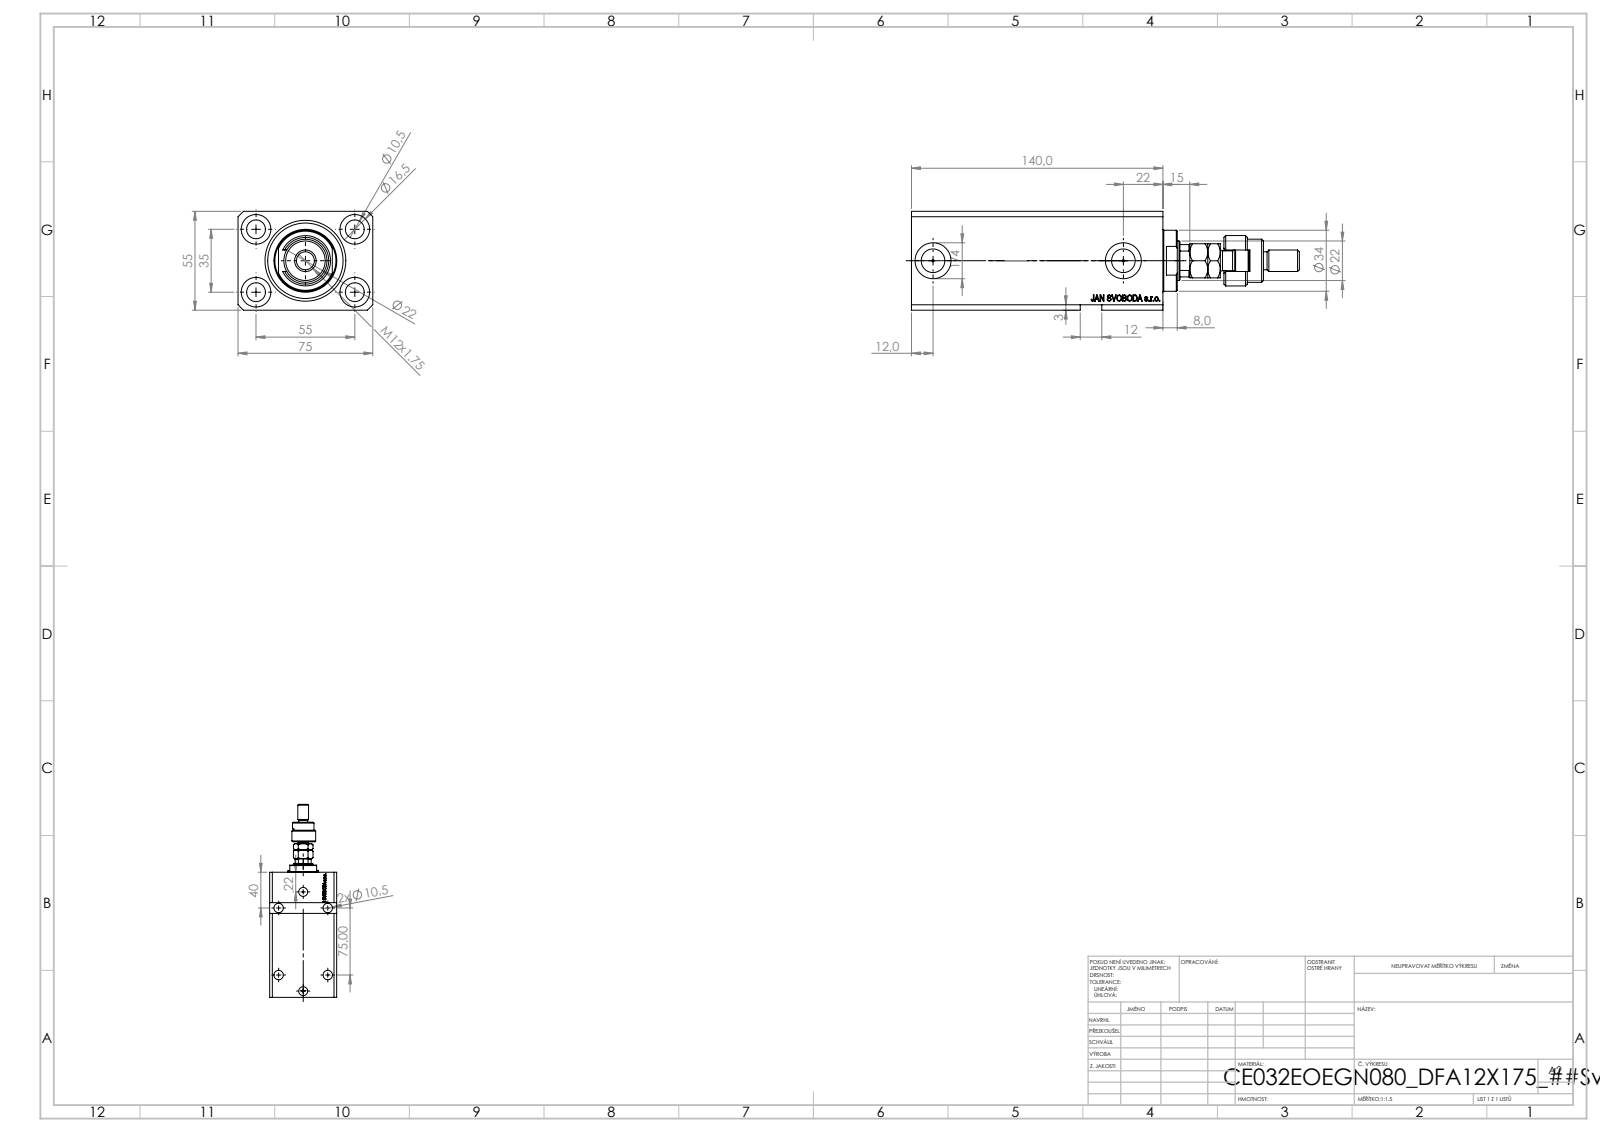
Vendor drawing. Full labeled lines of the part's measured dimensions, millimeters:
Part name (STEP PRODUCT): MFA; V250CE_E_Body; V250CE_C_VCP; FEMALE_PART_FOR_DFA (+1 more)
STEP written by: SolidWorks 2019 (CONFIG_CONTROL_DESIGN)
Units: millimetres
Bodies: 5 solids, 999 faces (466 planar, 117 cylindrical, 416 other)
Overall size (bounding box): 216 × 75 × 55
Volume: 487 089 mm³ · Surface area: 109 148 mm²
Round holes (diameter × count): ⌀10.5 ×9, ⌀1.25 ×4, ⌀16.5 ×4, ⌀10 ×2, ⌀13.16 ×2, ⌀20 ×2, ⌀22 ×1, ⌀32 ×1, ⌀45 ×1
Round bosses / shafts (diameter × count): ⌀34 ×1, ⌀28 ×1, ⌀24 ×1, ⌀18 ×1, ⌀12 ×1, ⌀11 ×1, ⌀10 ×1
Partial cylindrical surfaces — rounded edges, fillets, slot ends (radius × count): R9.75 ×1, R10.5 ×1
Main face-to-face distances: 55, 75, 15, 140, 125, 9.9, 115.1, 130.1, 19, 129
Hole centre spacings: 32.6, 32.87, 55, 96.98, 32.58, 35, 65.19, 75
